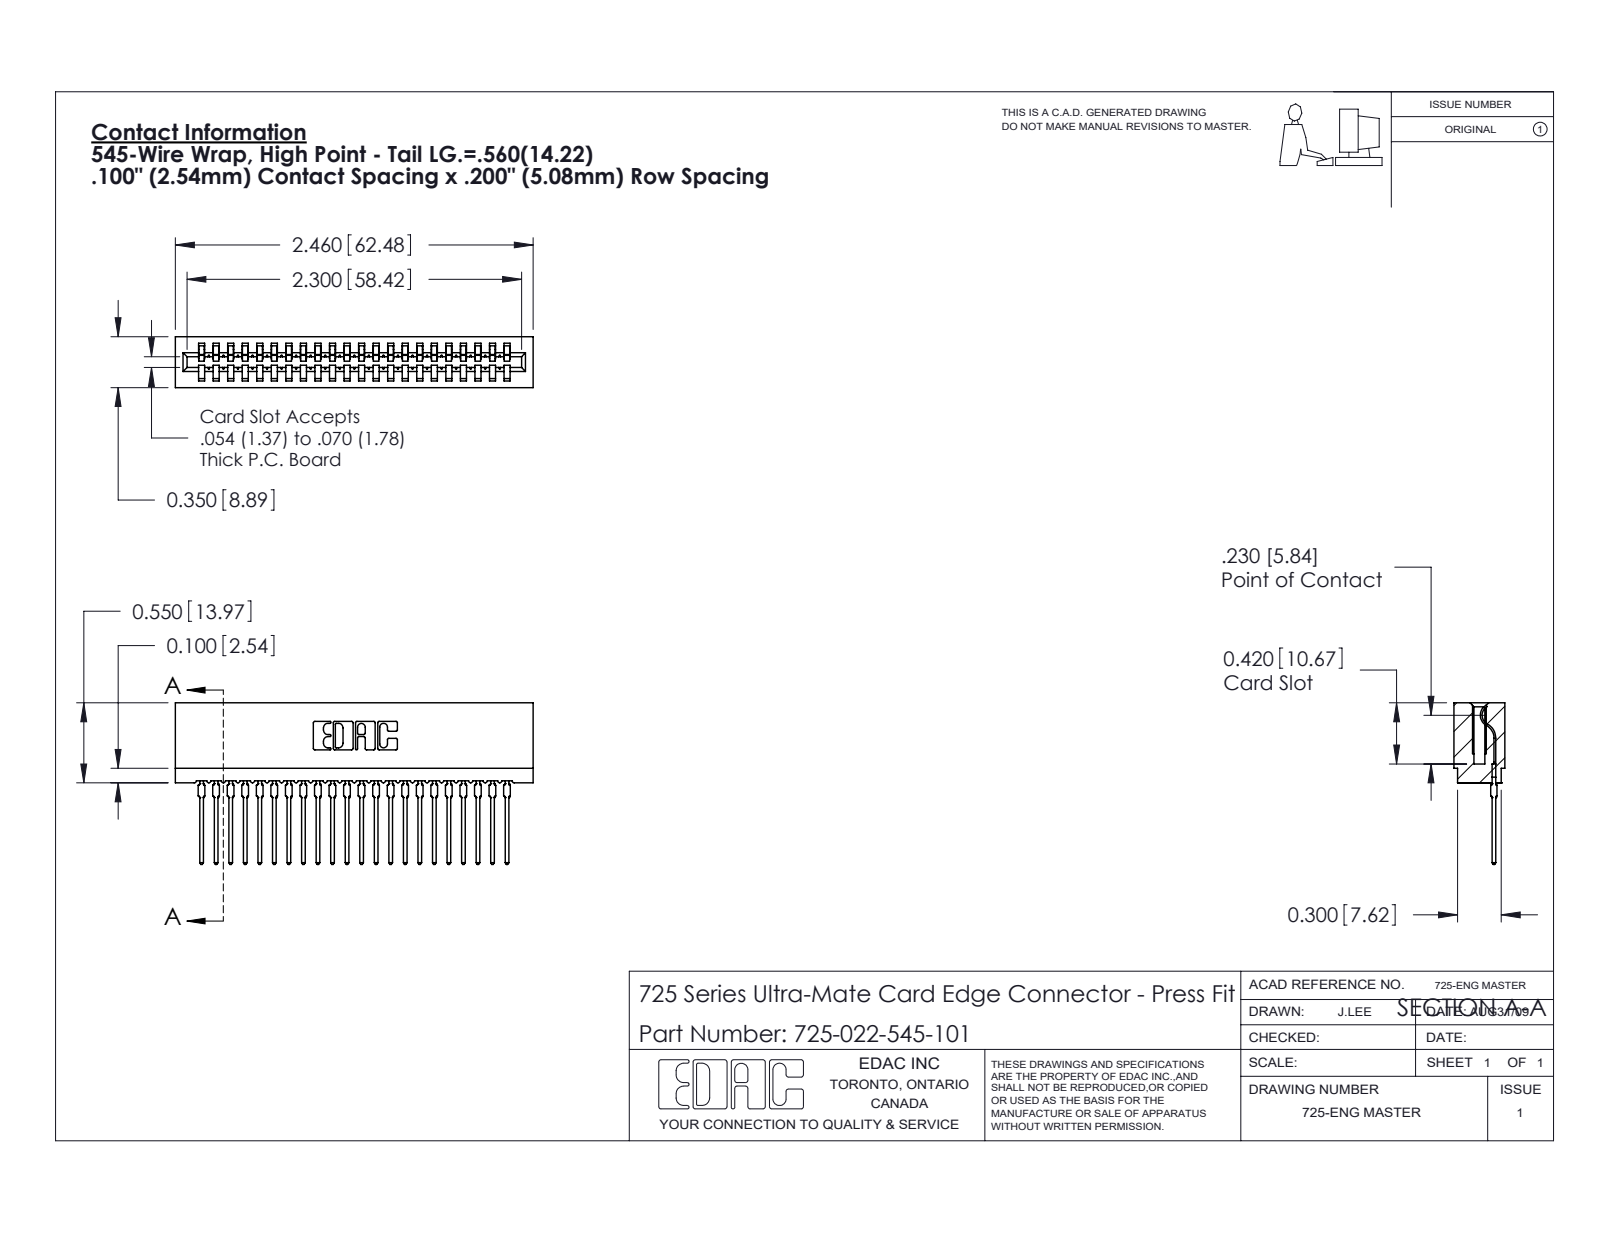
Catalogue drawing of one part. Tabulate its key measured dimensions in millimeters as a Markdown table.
| quantity | value |
| --- | --- |
| part name | 725 Part_Insulator Option - 01; 745-292-001_545; 725-022-545-101 |
| STEP written by | SolidWorks 2020 (CONFIG_CONTROL_DESIGN) |
| units | millimeters |
| bodies | 23 solids, 2559 faces (1529 planar, 458 cylindrical, 572 other) |
| overall size | 62.5 × 28.2 × 8.9 |
| volume | 4 920 mm³ |
| surface area | 9 426 mm² |
| partial cylindrical surfaces (radius × count) | 0.4 × 44, 0.5 × 44, 0.3 × 22, 0.2 × 6, 0.8 × 6, 0.1 × 4, 0.3 × 4, 0.7 × 3 |
| main face-to-face distances | 2.5, 5.1, 7.6, 8.9, 10.2, 15.2, 17.8, 12.7, 1.6, 7.3 |
